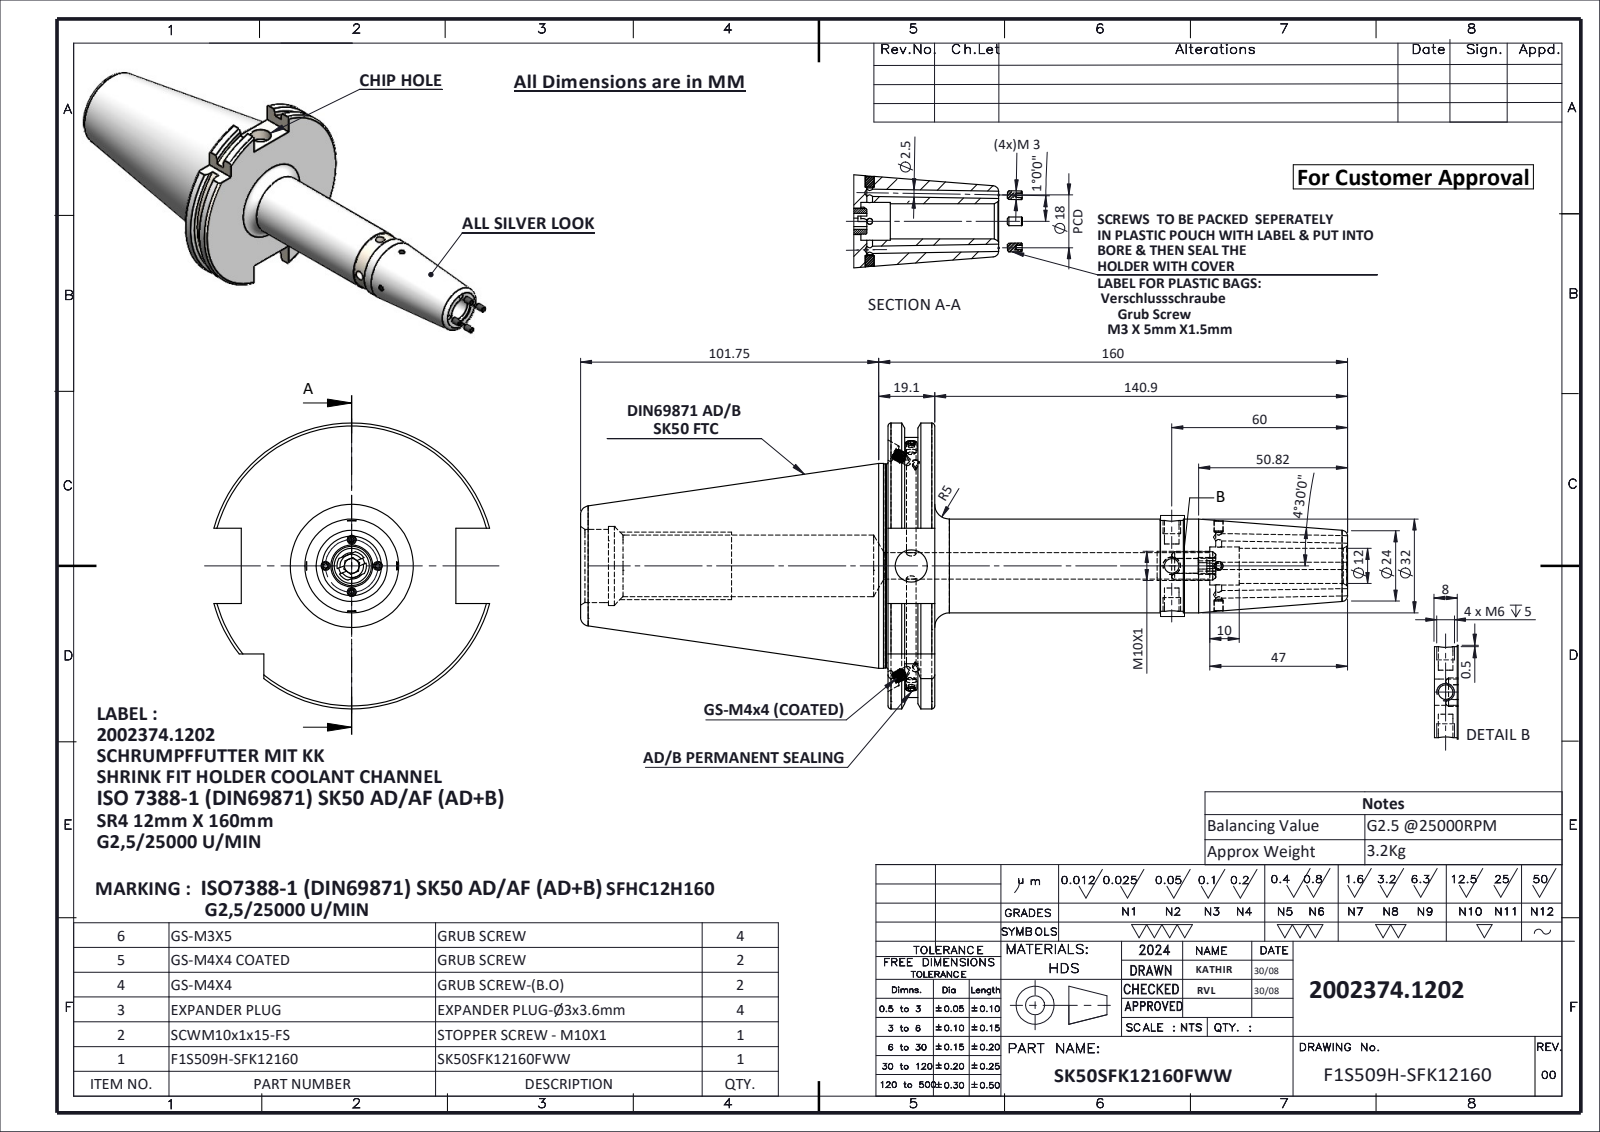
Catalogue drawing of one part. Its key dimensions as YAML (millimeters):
part_name: "F1S509H-SFK12160; SCWM10x1x15-FLAT&SLOT; GS-M3X5; EXPANDER PLUG Ø3x3.6 (+3 more)"
step_written_by: "SolidWorks 2024 (CONFIG_CONTROL_DESIGN)"
units: millimeters
bodies: {solids: 14, faces: 465, planar: 156, cylindrical: 139, other: 170}
overall_size: [269.77, 97.5, 94.05]
volume: 415283
surface_area: 65746
round_holes:
  - {diameter: 2.5, count: 4}
  - {diameter: 5, count: 3}
  - {diameter: 2, count: 2}
  - {diameter: 3, count: 2}
  - {diameter: 3.2, count: 2}
  - {diameter: 6, count: 2}
  - {diameter: 3.3, count: 1}
  - {diameter: 9, count: 1}
  - {diameter: 11, count: 1}
  - {diameter: 11.98, count: 1}
  - {diameter: 12.98, count: 1}
  - {diameter: 21, count: 1}
round_bosses_or_shafts:
  - {diameter: 4, count: 4}
  - {diameter: 3, count: 4}
  - {diameter: 2.9, count: 2}
  - {diameter: 69.85, count: 1}
  - {diameter: 69.45, count: 1}
  - {diameter: 32, count: 1}
  - {diameter: 31, count: 1}
partial_cylinders:
  - {radius: 5, count: 1}
  - {radius: 44.9, count: 1}
  - {radius: 48.75, count: 1}
face_to_face_distances: [15.9, 5.66, 10.24, 10.14, 4.48, 5.76, 104.95, 110.61, 115.09, 120.85]
hole_center_spacings: [16, 88.9, 104.9]
